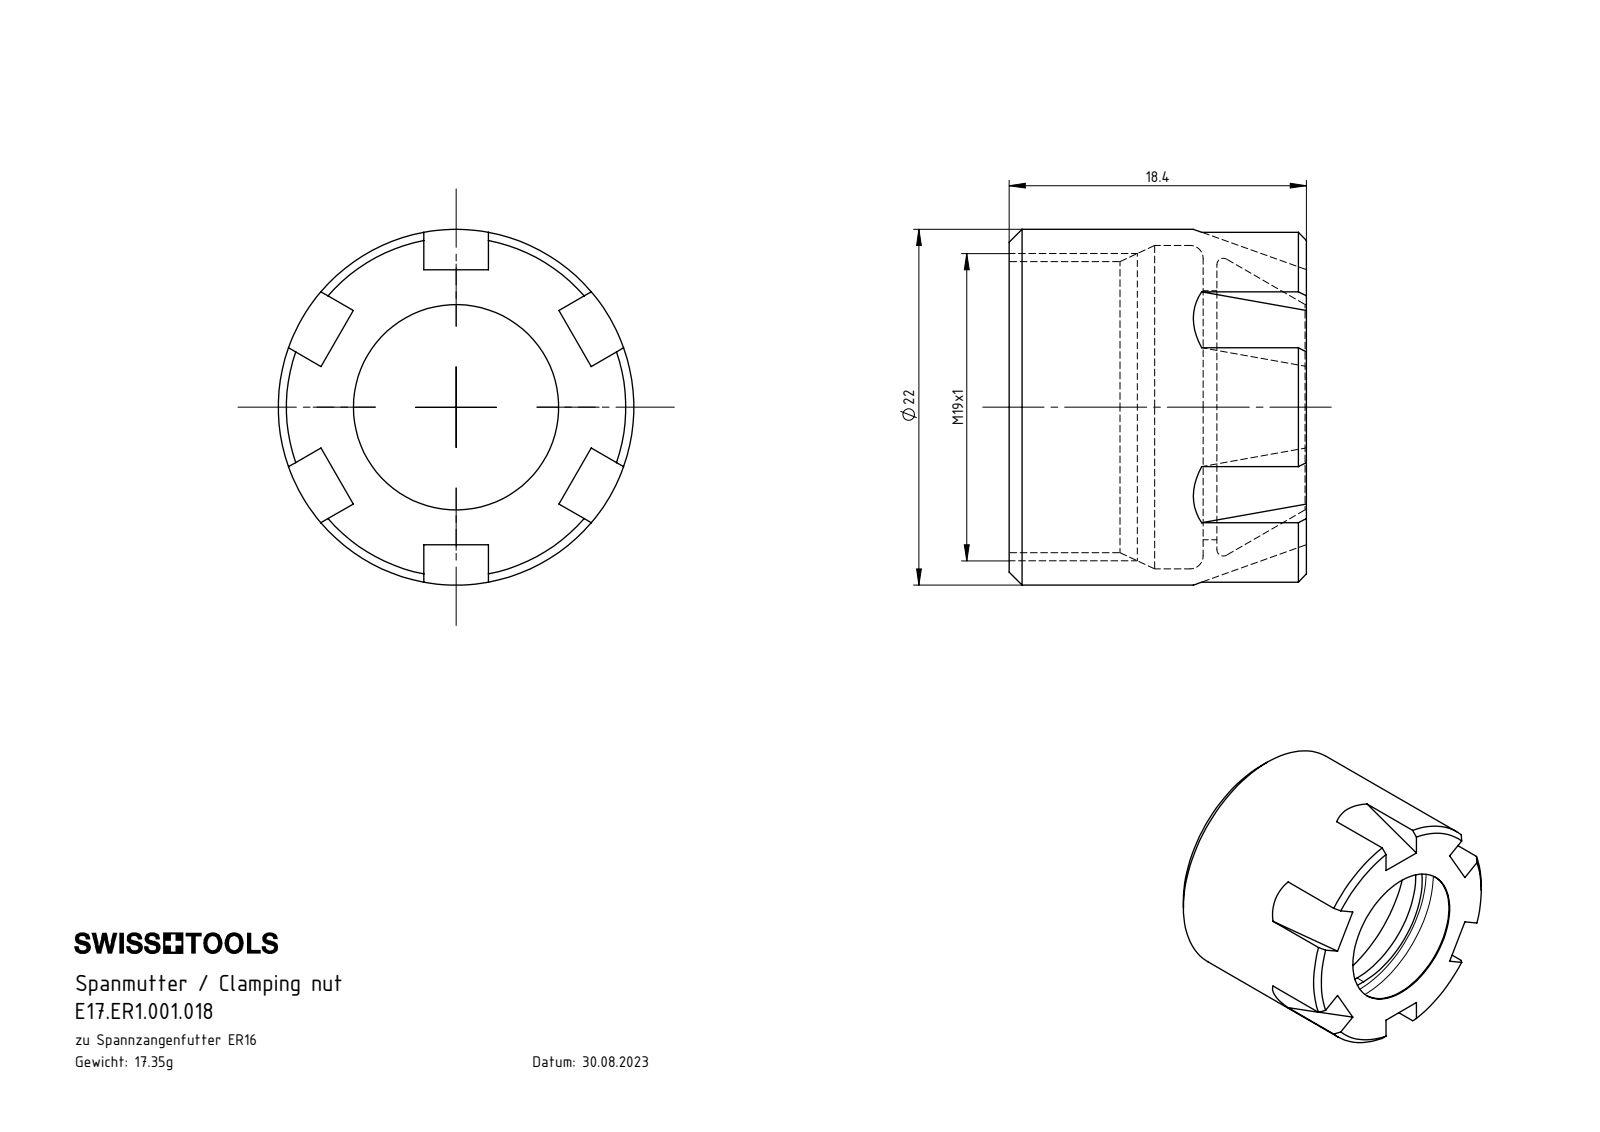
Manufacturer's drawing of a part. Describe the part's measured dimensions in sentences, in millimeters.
The part is named "E17.ER1.001.018". Its 3-D file was written by "SolidWorks 2017 (AUTOMOTIVE_DESIGN)". It is 1 solid with 52 faces: 24 planar, 11 cylindrical and 17 other. Overall it measures 22 by 22 by 18.4 millimeters. Its volume is 2 210 cubic millimeters and its surface area 2 855 square millimeters. Round holes: 1 of diameter 12.7, 1 of diameter 18, 1 of diameter 20. Round bosses or shafts: 1 of diameter 22. Partial cylindrical surfaces (rounded edges, fillets, slot ends): 2 of radius 7.7. The main face-to-face distances are 18.4, 12, 6.4, 4, 12.85, 0.85, 5.55, 15.4.
